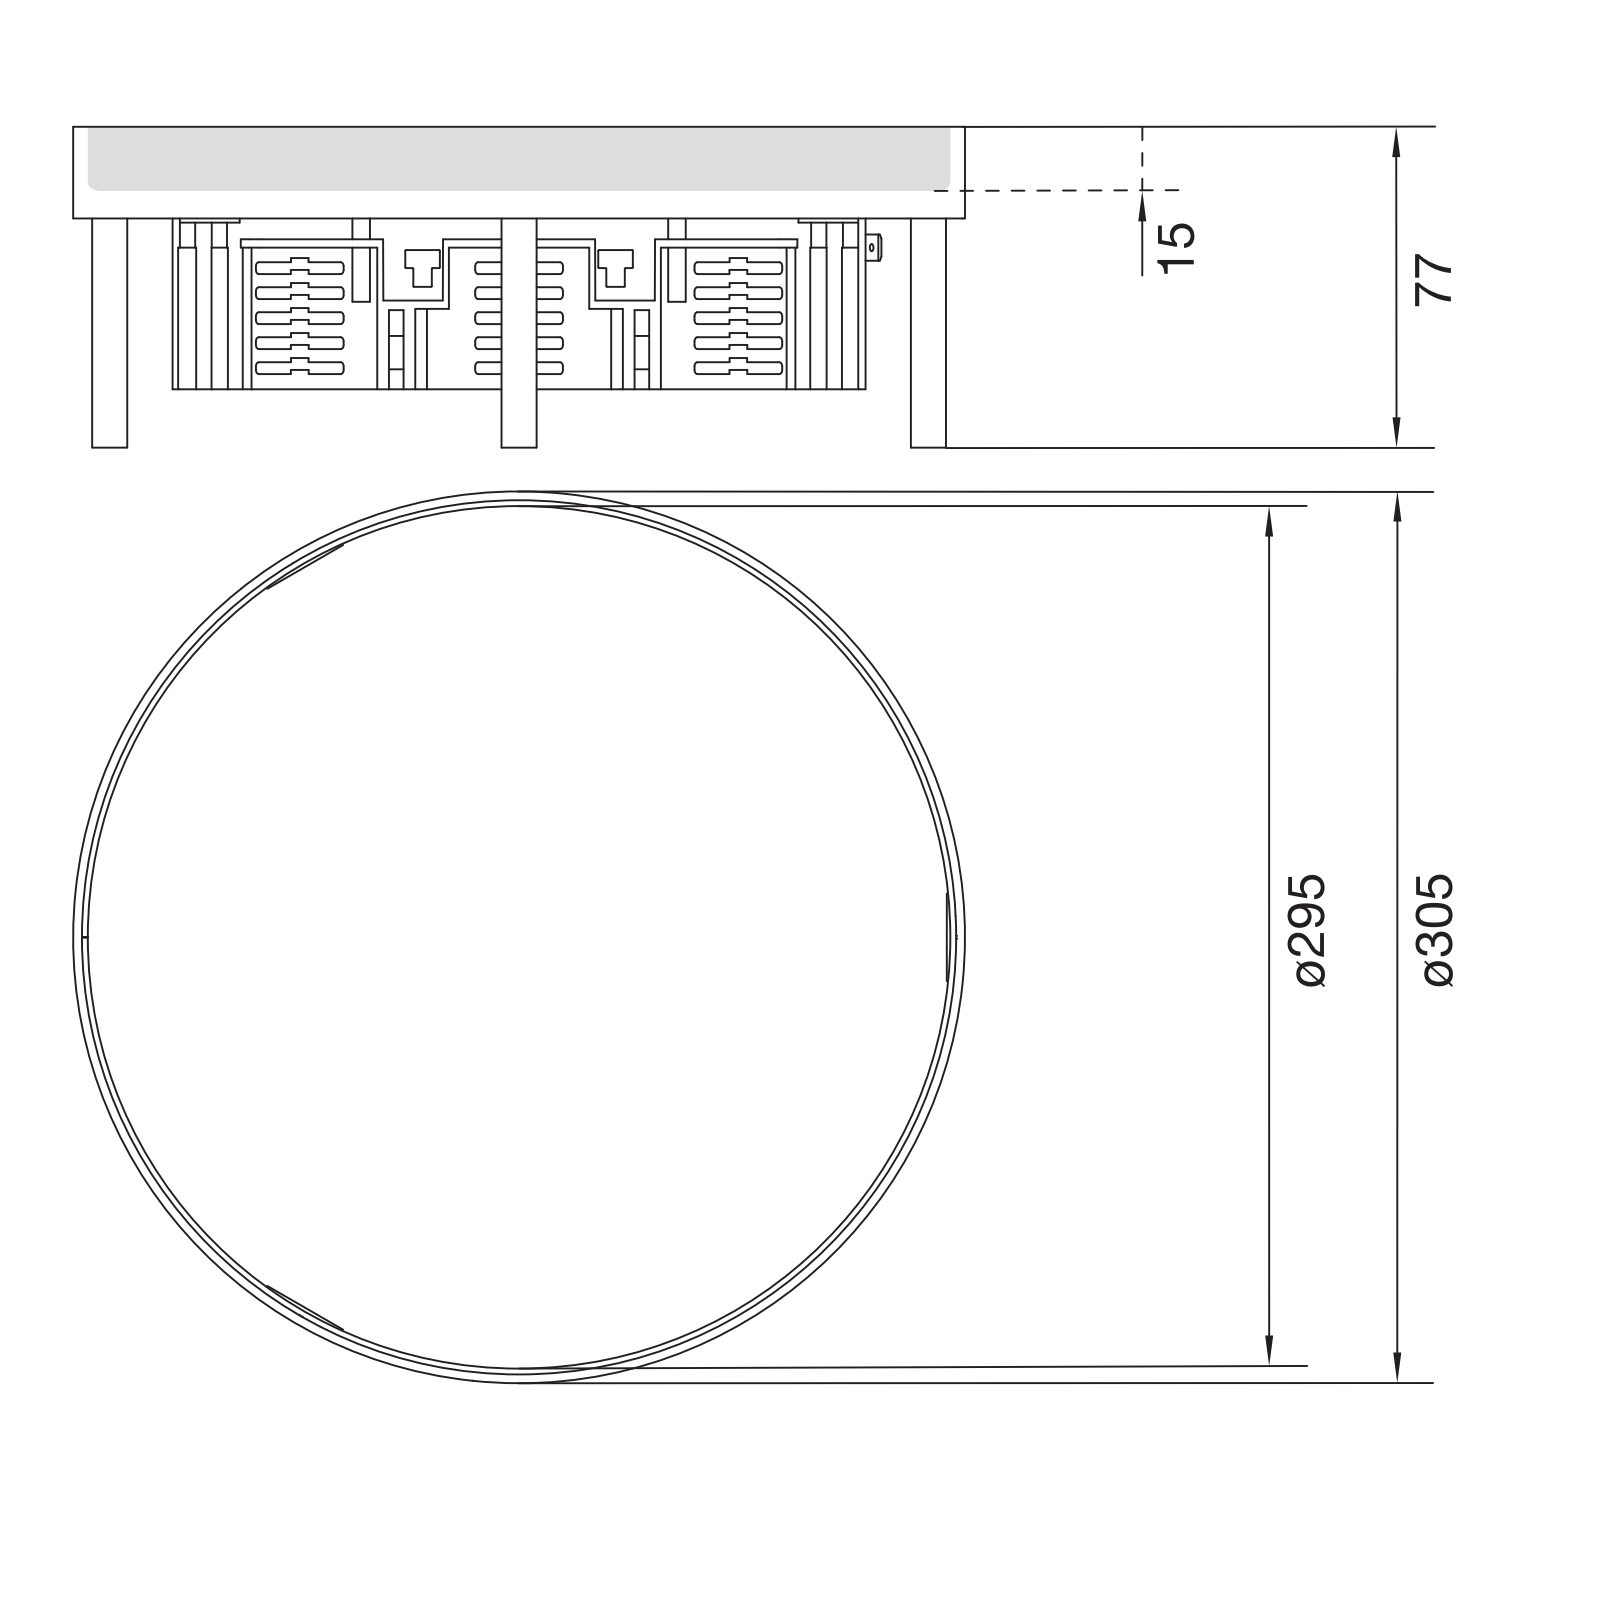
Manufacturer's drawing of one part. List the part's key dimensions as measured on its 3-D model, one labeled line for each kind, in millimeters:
Part name (STEP PRODUCT): T-00702; T-00703; T-00704; T-00708 (+8 more)
STEP written by: CREO PARAMETRIC BY PTC INC, 2022024 (AUTOMOTIVE_DESIGN)
Units: millimetres
Bodies: 8 solids, 132 faces (72 planar, 60 cylindrical, 0 other)
Overall size (bounding box): 305 × 305 × 77
Volume: 340 119 mm³ · Surface area: 387 738 mm²
Round holes (diameter × count): ⌀3.8 ×6, ⌀10.1 ×4
Round bosses / shafts (diameter × count): ⌀12 ×4, ⌀9.85 ×4, ⌀305 ×1, ⌀301 ×1, ⌀299 ×1, ⌀295 ×1
Partial cylindrical surfaces — rounded edges, fillets, slot ends (radius × count): R0.5 ×8, R150 ×1
Main face-to-face distances: 2, 2.5, 5, 7, 228.5, 3, 229.5, 226, 231, 227
Hole centre spacings: 59.51, 143.6, 197.99, 225.52, 260.65, 25.3, 108, 123.66
